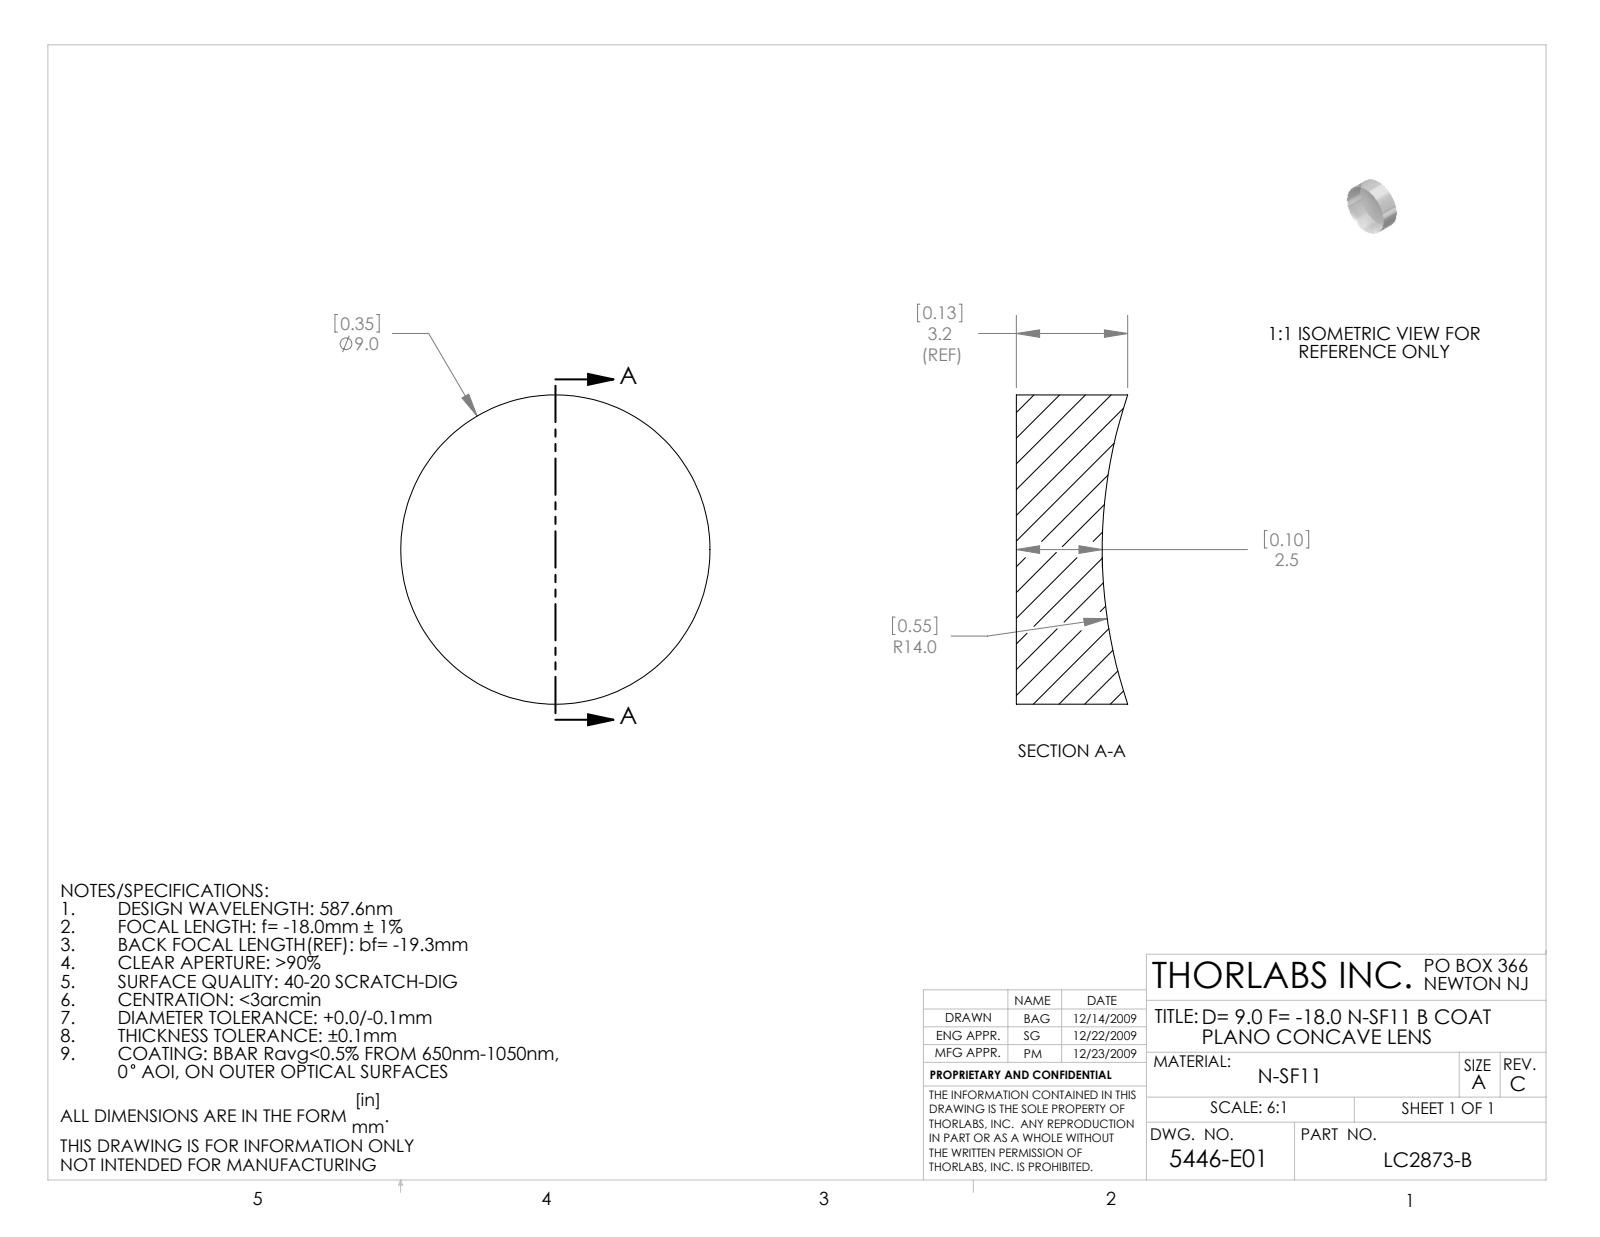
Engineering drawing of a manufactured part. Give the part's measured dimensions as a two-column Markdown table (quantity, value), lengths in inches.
| quantity | value |
| --- | --- |
| part name | 5446-E0W |
| STEP written by | SolidWorks 2009 (AUTOMOTIVE_DESIGN) |
| units | inches |
| bodies | 1 solid, 5 faces (1 planar, 2 cylindrical, 2 other) |
| overall size | 0.354 × 0.354 × 0.128 |
| volume | 0.011 in³ |
| surface area | 0.342 in² |
| round bosses / shafts (diameter × count) | 0.354 × 1 |
